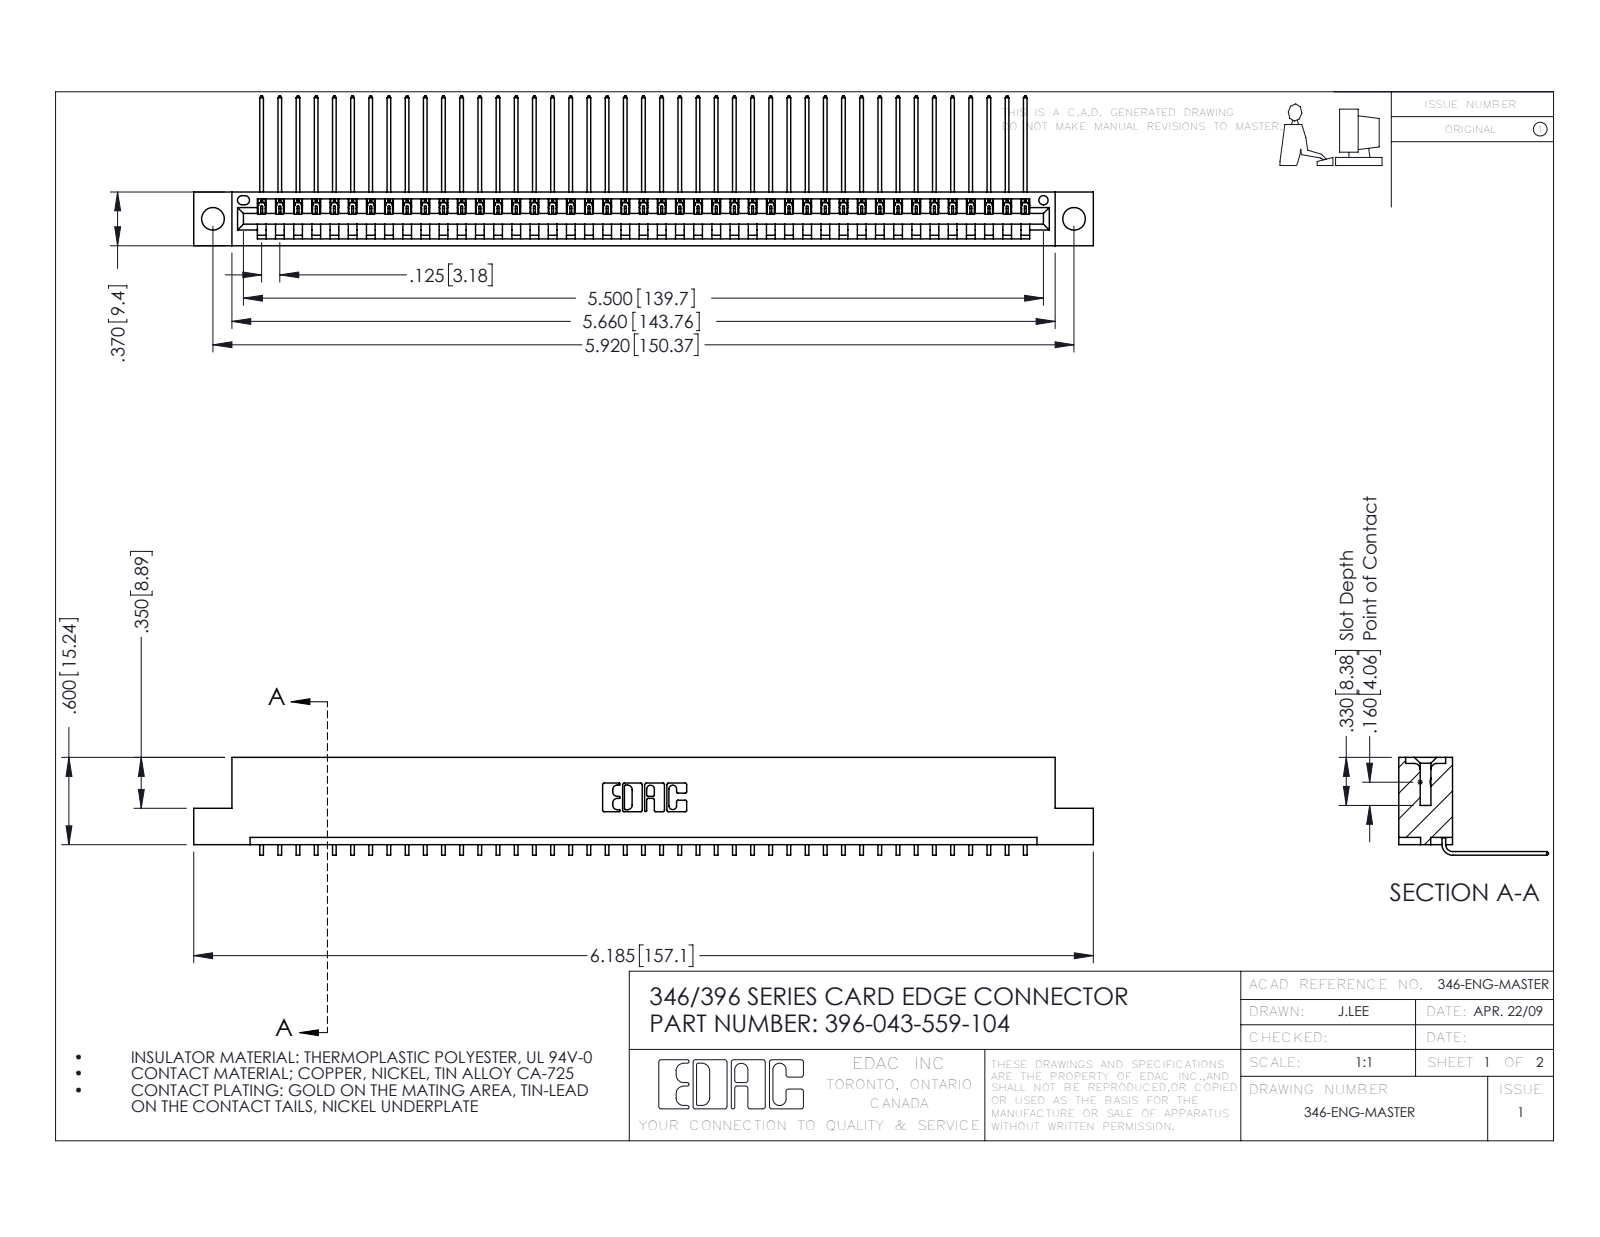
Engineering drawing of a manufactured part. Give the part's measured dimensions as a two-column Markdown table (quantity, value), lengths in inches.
| quantity | value |
| --- | --- |
| part name | 346 Part_Flush Mounting Lugs - 0.156 Dia-TH; 345-292-001_558 559 Tail - 1; 396-043-559-104 |
| STEP written by | SolidWorks 2016 (CONFIG_CONTROL_DESIGN) |
| units | inches |
| bodies | 44 solids, 2702 faces (1882 planar, 820 cylindrical, 0 other) |
| overall size | 6.185 × 1.03 × 0.673 |
| volume | 0.921 in³ |
| surface area | 30.29 in² |
| round holes (diameter × count) | 0.156 × 2, 0.064 × 1 |
| partial cylindrical surfaces (radius × count) | 0.006 × 86, 0.01 × 22, 0.007 × 6, 0.031 × 6, 0.026 × 3, 0.031 × 2, 0.04 × 2, 0.014 × 1 |
| main face-to-face distances | 0.048, 0.322, 0.37, 0.025, 0.25, 0.072, 0.298, 0.148, 0.222, 0.1 |
| hole center spacings | 0.246, 5.711, 5.92 |
